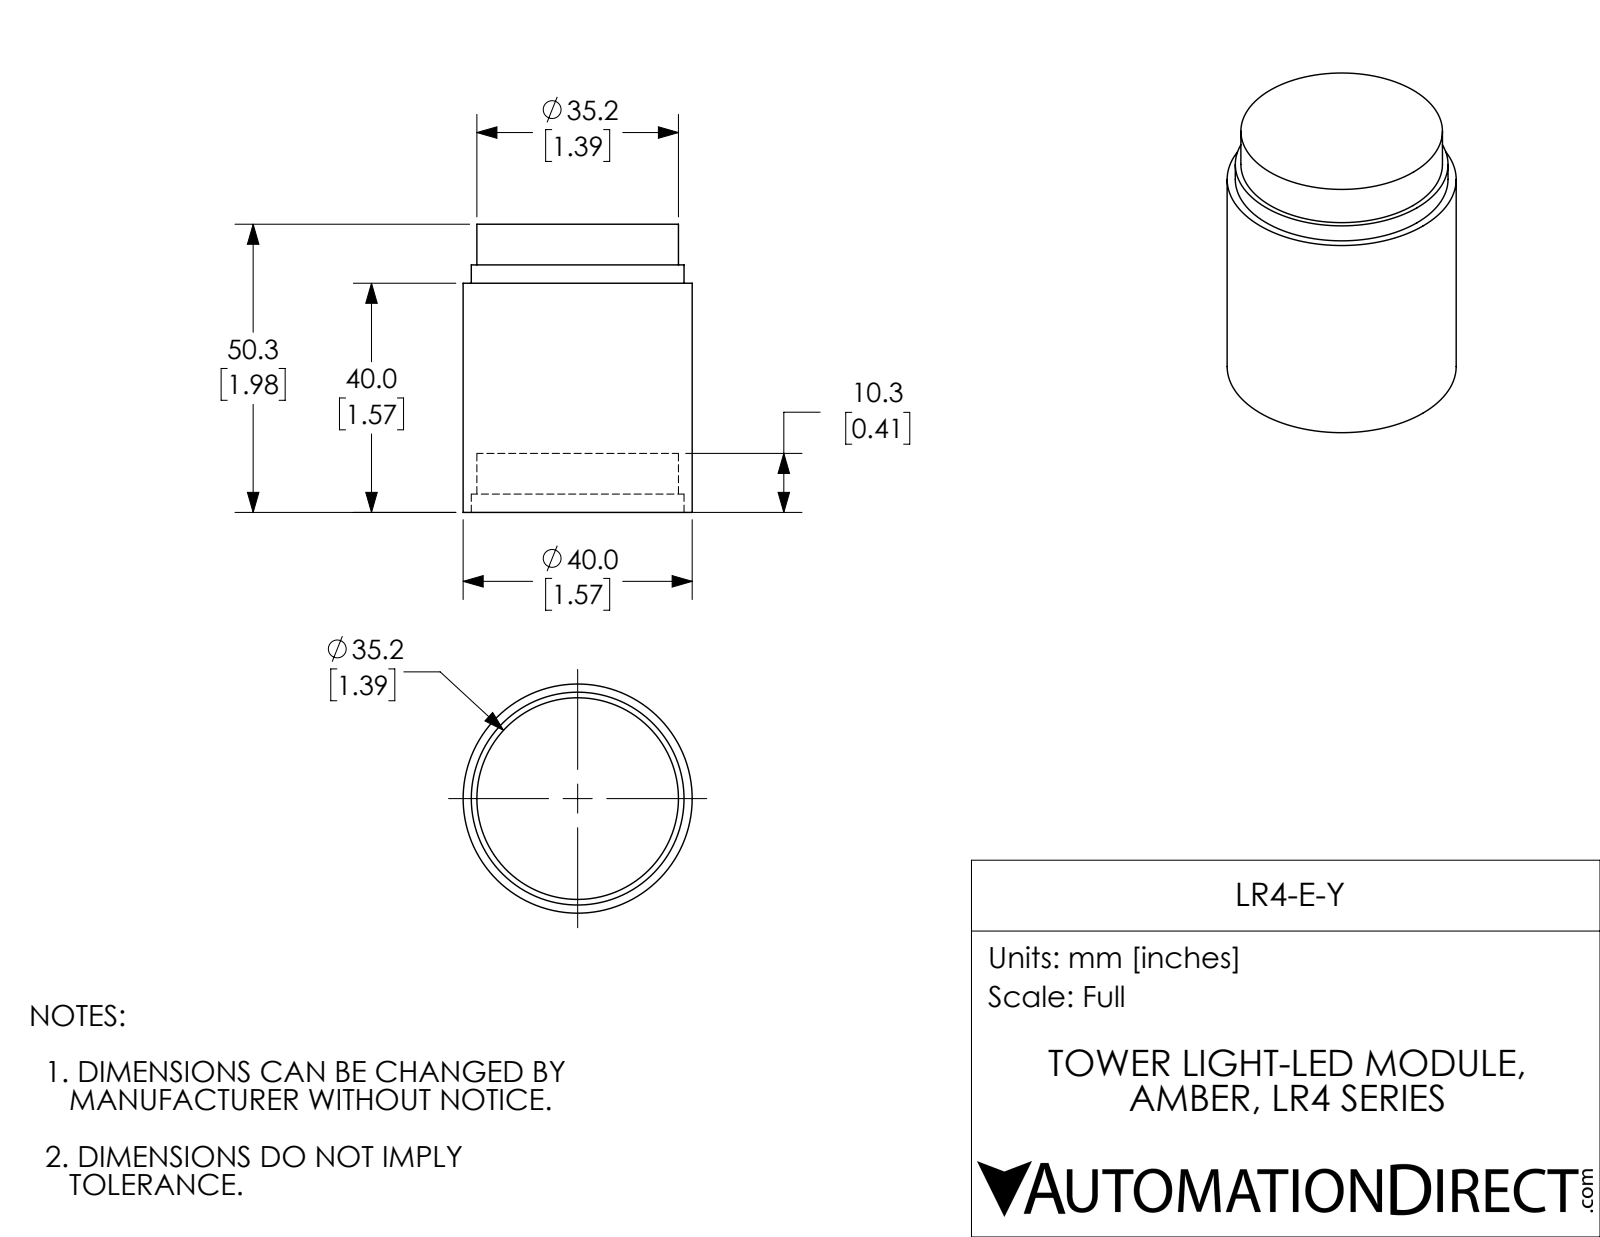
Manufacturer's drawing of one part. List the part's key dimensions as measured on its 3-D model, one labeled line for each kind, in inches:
Part name (STEP PRODUCT): LR4-E-Y
STEP written by: SolidWorks 2017 (AUTOMOTIVE_DESIGN)
Units: inches
Bodies: 1 solid, 16 faces (6 planar, 10 cylindrical, 0 other)
Overall size (bounding box): 1.98 × 1.575 × 1.575
Volume: 3.067 in³ · Surface area: 15.28 in²
Round holes (diameter × count): ⌀1.386 ×1, ⌀1.463 ×1
Round bosses / shafts (diameter × count): ⌀1.575 ×1
Main face-to-face distances: 1.575, 0.406, 0.126, 0.28, 1.98, 1.169, 1.701, 1.295, 1.449, 1.854
